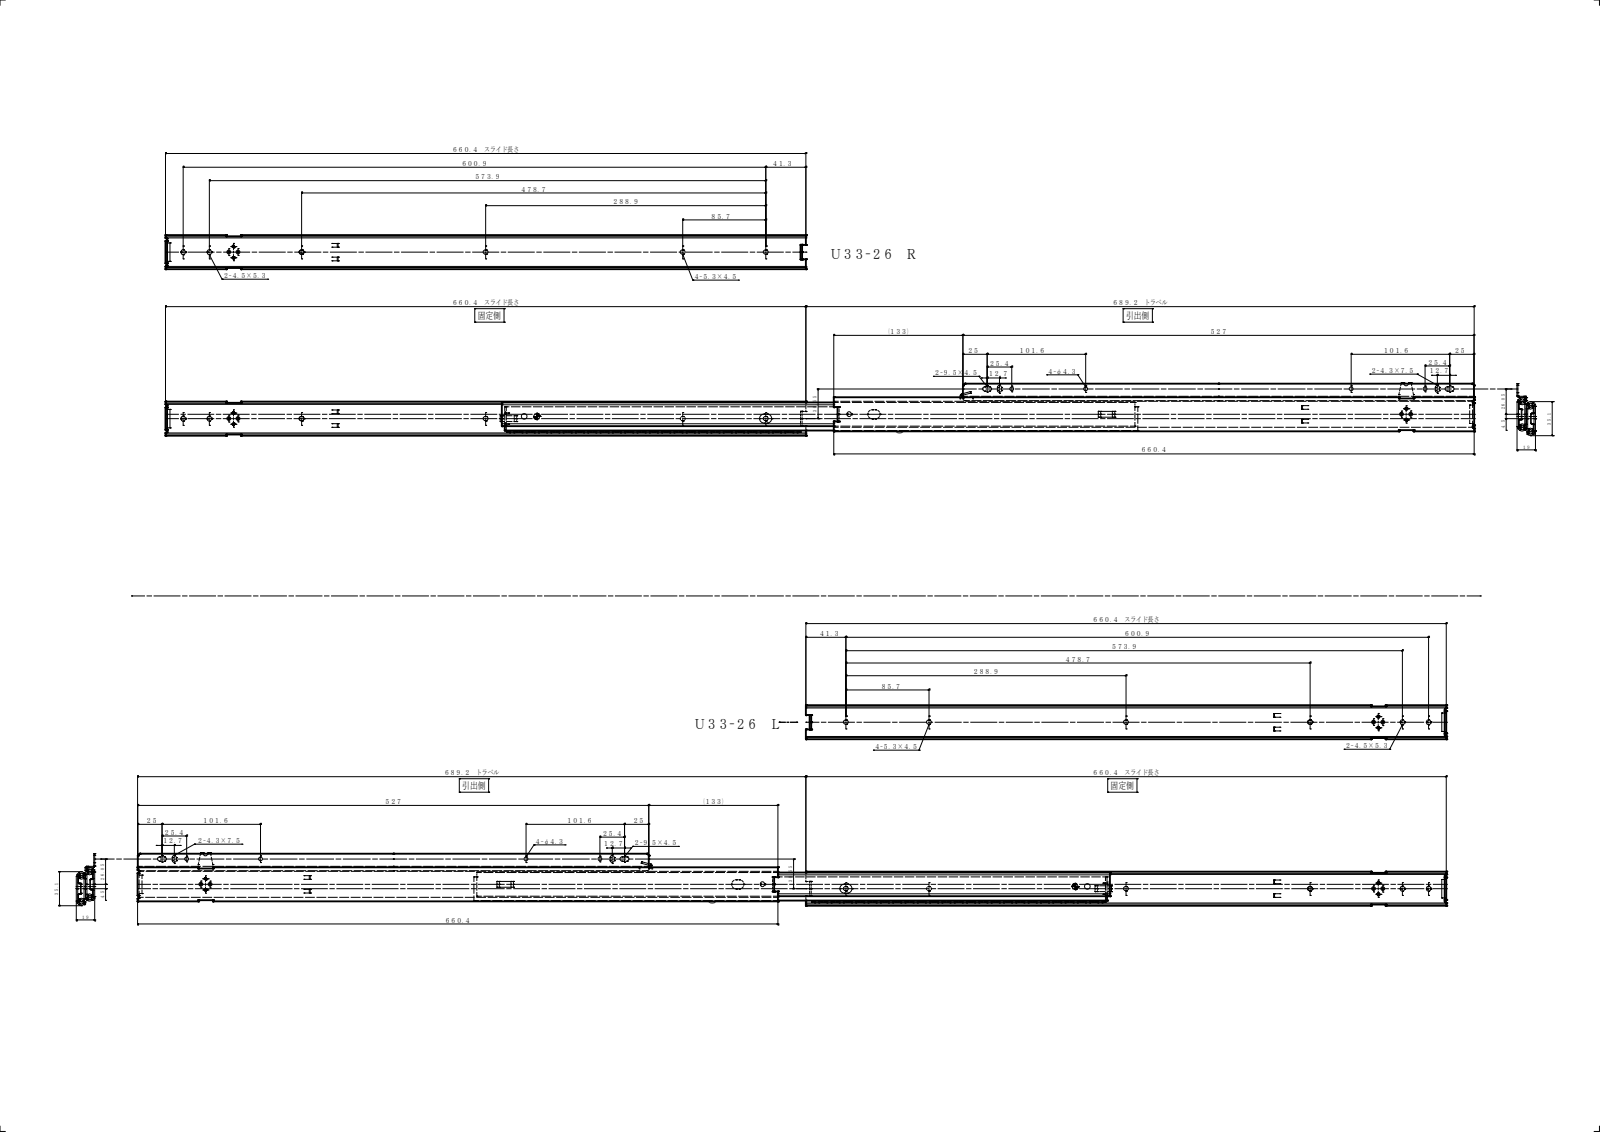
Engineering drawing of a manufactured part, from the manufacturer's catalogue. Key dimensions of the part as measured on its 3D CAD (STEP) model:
Part name (STEP PRODUCT): PN41-3; U33-26Lドロ側OM; PN26; U33-26L@R (+8 more)
STEP written by: SolidWorks 2019 (CONFIG_CONTROL_DESIGN)
Units: millimetres
Bodies: 20 solids, 1094 faces (634 planar, 432 cylindrical, 28 other)
Overall size (bounding box): 1349.4 × 450 × 54.75
Volume: 339 853 mm³ · Surface area: 495 036 mm²
Round holes (diameter × count): ⌀2.3 ×4, ⌀2.7 ×4, ⌀4.2 ×4, ⌀4.3 ×4, ⌀2.4 ×2, ⌀2.8 ×2, ⌀4.5 ×2
Partial cylindrical surfaces — rounded edges, fillets, slot ends (radius × count): R2 ×32, R0.5 ×28, R0.4 ×24, R1 ×24, R2.25 ×18, R1.5 ×14, R0.3 ×12, R1.3 ×8
Main face-to-face distances: 1.5, 9.5, 8, 431, 421.5, 17.5, 423, 439, 429.5, 432.5
Hole centre spacings: 7.46, 16.06, 1208.17, 9.5, 10.25, 11.5, 19.75, 152.4
